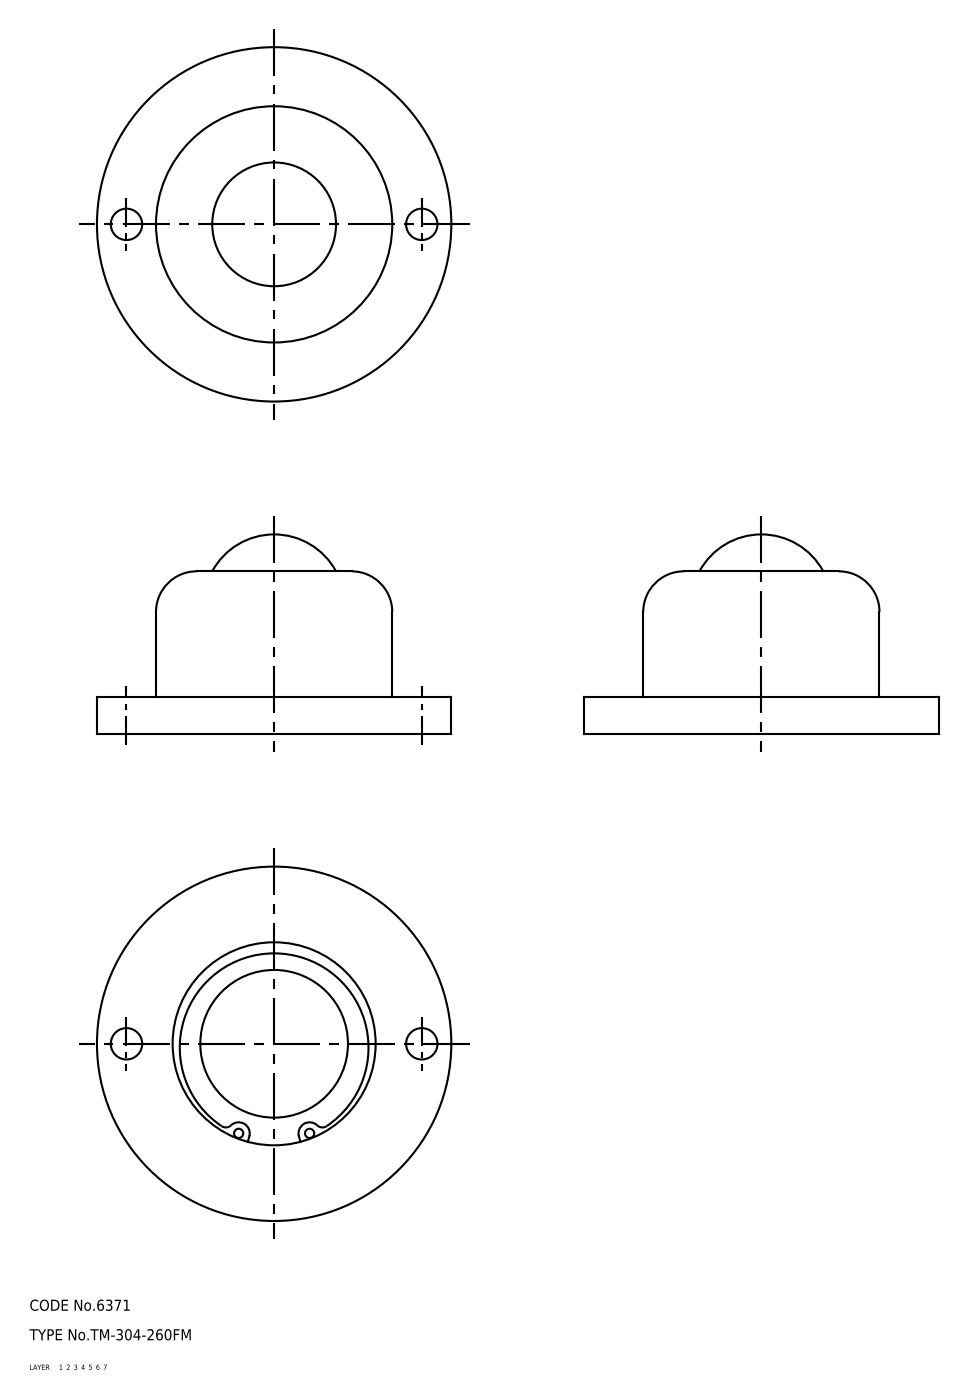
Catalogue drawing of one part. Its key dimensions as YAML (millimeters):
part_name: "67112276; 67112289"
step_written_by: "CADfix (AUTOMOTIVE_DESIGN)"
units: millimeters
bodies: {solids: 2, faces: 43, planar: 0, cylindrical: 0, other: 43}
overall_size: [96, 96, 54]
volume: 100936
surface_area: 39540
